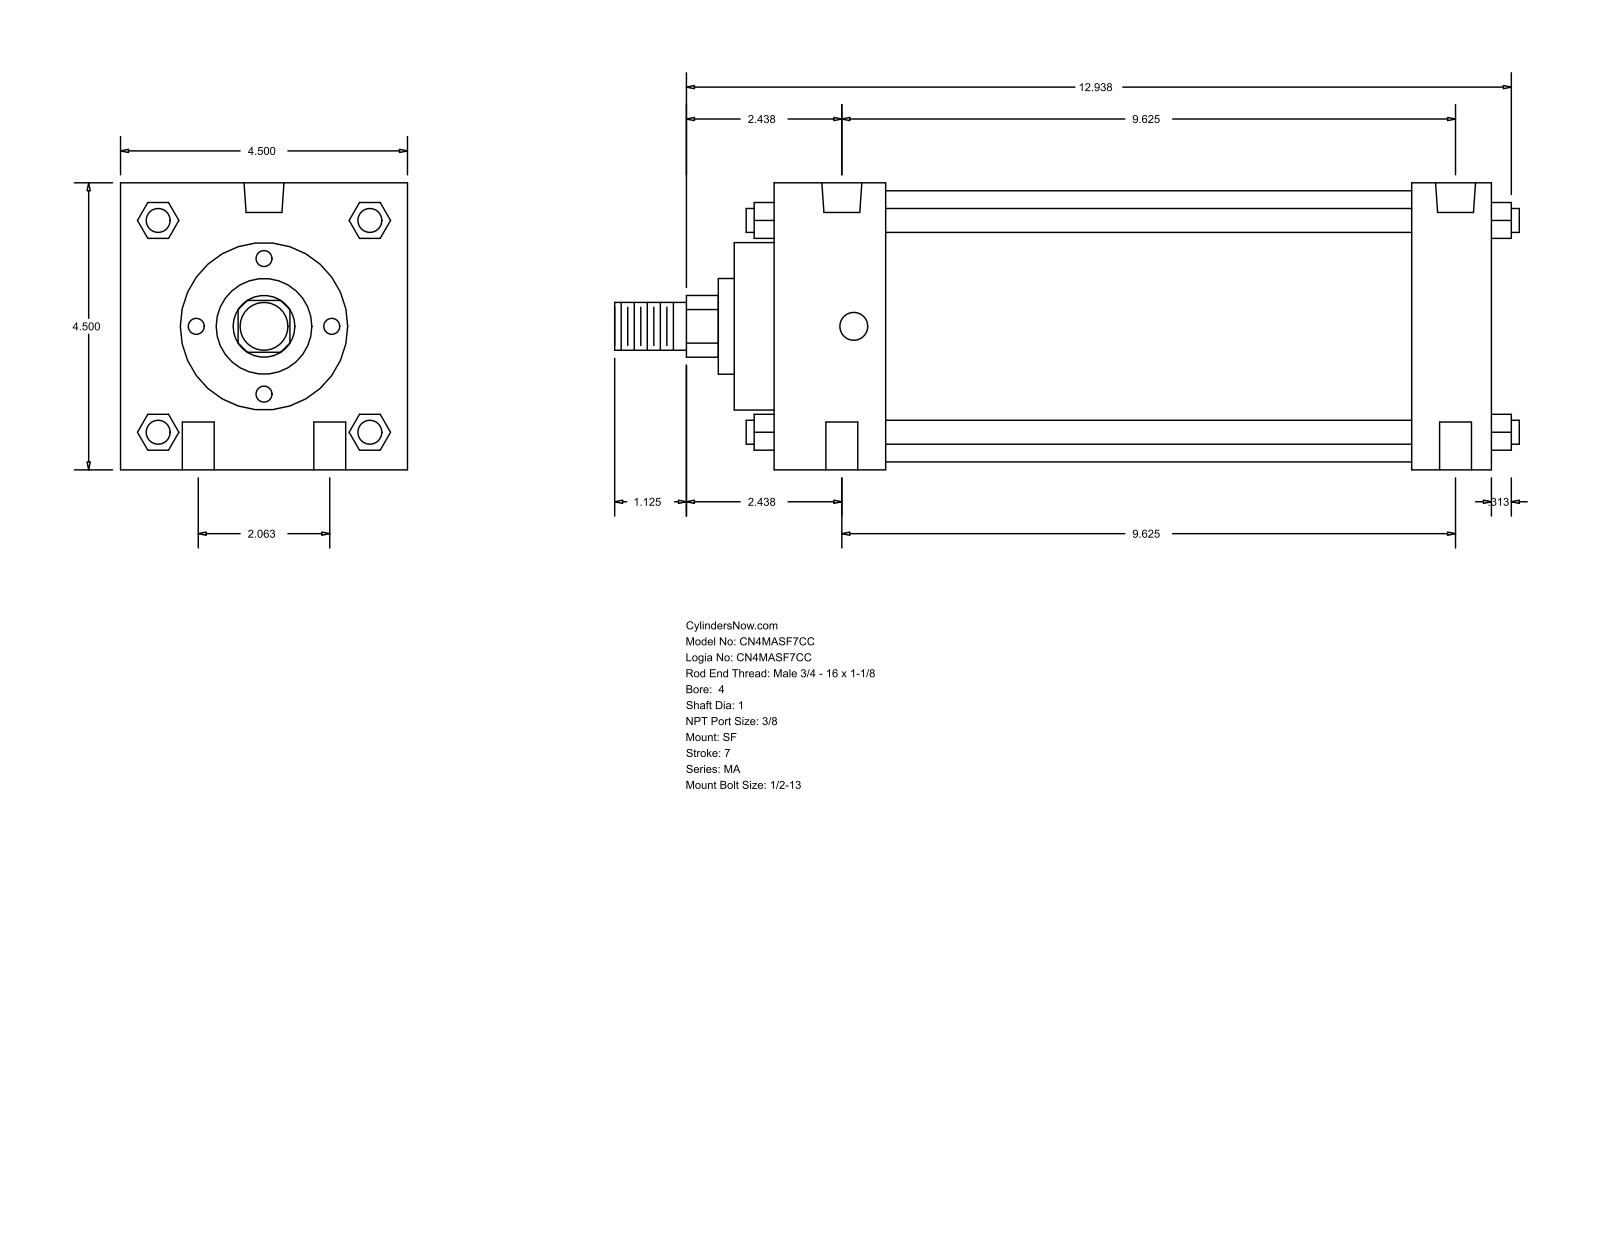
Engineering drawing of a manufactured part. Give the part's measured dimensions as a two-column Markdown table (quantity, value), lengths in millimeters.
| quantity | value |
| --- | --- |
| part name | MA_SF__0400_1 |
| STEP written by | GSSL Pune (CONFIG_CONTROL_DESIGN) |
| units | millimeters |
| bodies | 0 solids, 126 faces (95 planar, 31 cylindrical, 0 other) |
| overall size | 360.36 × 114.3 × 114.3 |
| round holes (diameter × count) | 12.7 × 4, 11.11 × 2, 15.93 × 2 |
| round bosses / shafts (diameter × count) | 9.53 × 4, 107.95 × 1, 66.67 × 1, 38.1 × 1, 25.4 × 1, 19.05 × 1 |
| partial cylindrical surfaces (radius × count) | 12.29 × 1 |
| main face-to-face distances | 114.3, 285.76, 254.01, 31.75, 44.46, 209.55, 241.3, 15.87, 60.33, 269.88 |
| hole center spacings | 26.19, 245.88, 244.48, 52.38, 250.03, 234.95 |
